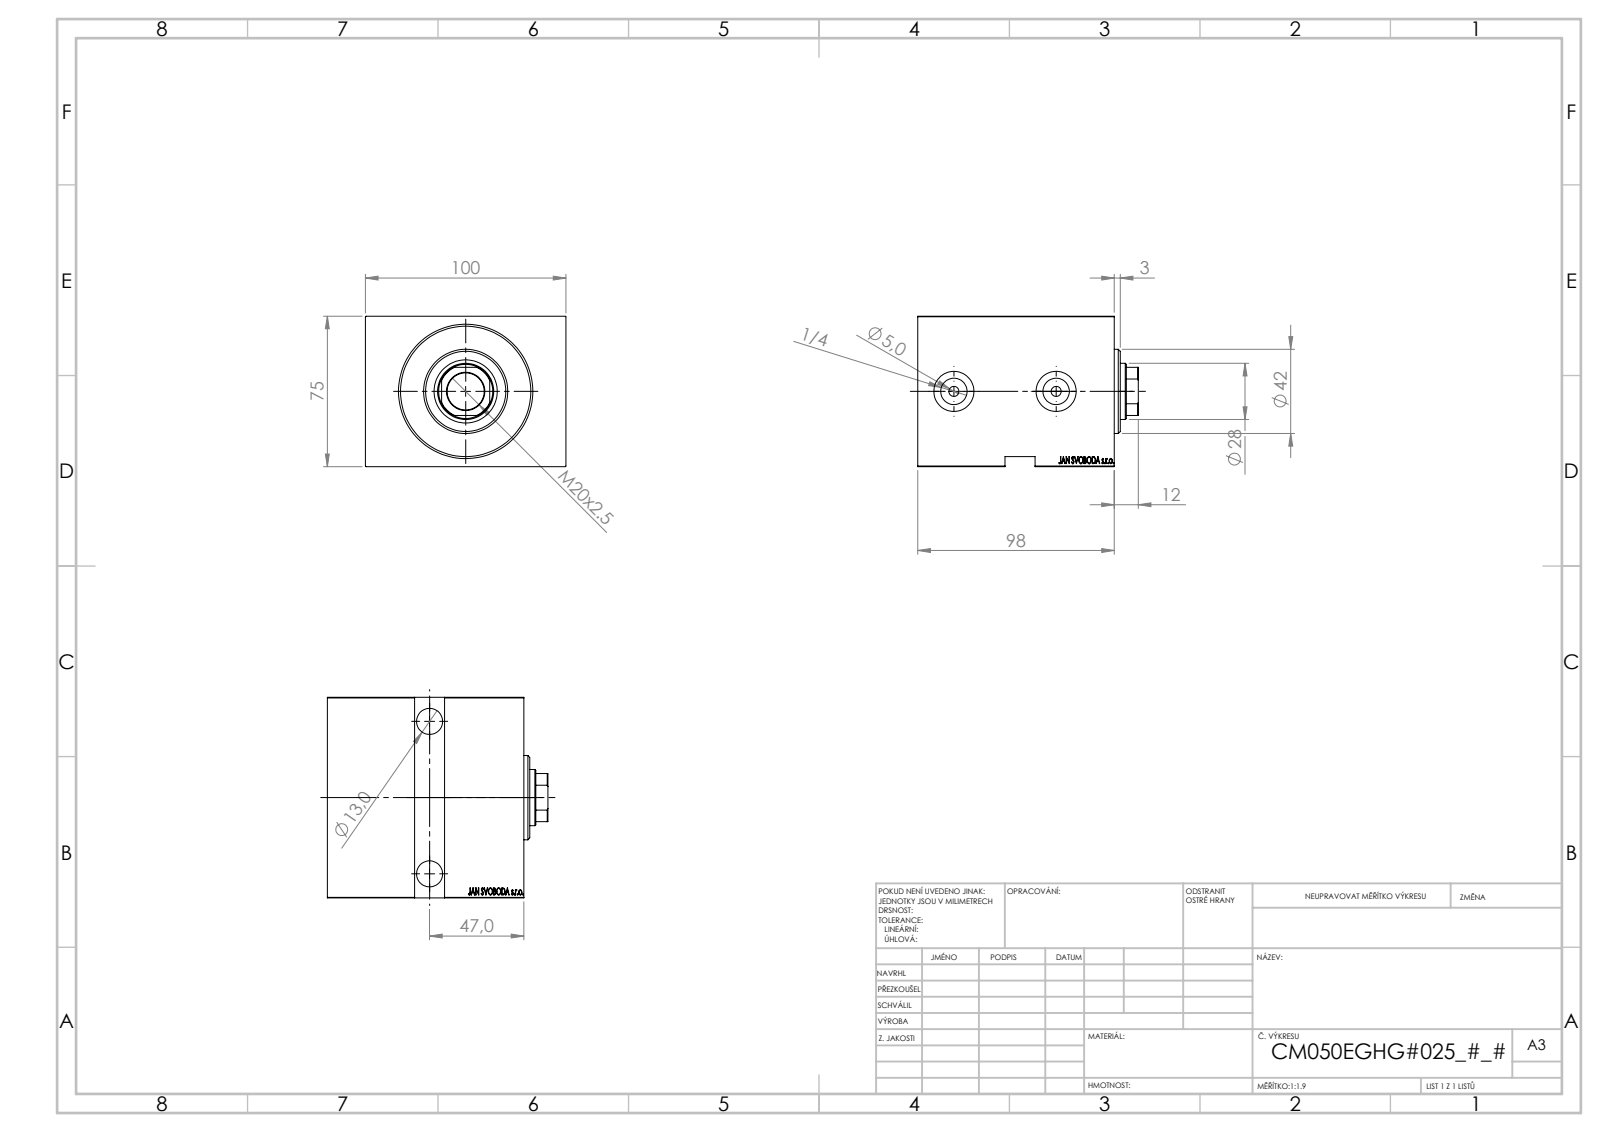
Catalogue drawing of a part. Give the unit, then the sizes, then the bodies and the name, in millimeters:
Units: millimetres
Overall size (bounding box): 110 × 100 × 75
Round holes (diameter × count): ⌀5 ×2, ⌀13 ×2, ⌀13.16 ×2, ⌀19 ×2, ⌀20 ×2, ⌀18.5 ×1, ⌀28 ×1, ⌀31.5 ×1, ⌀50 ×1, ⌀65 ×1
Round bosses / shafts (diameter × count): ⌀52 ×1, ⌀42 ×1
Partial cylindrical surfaces — rounded edges, fillets, slot ends (radius × count): R13.5 ×1
Main face-to-face distances: 75, 100, 98, 14, 84, 5, 93, 79, 81.4, 67.4
Hole centre spacings: 51, 76
Volume: 674 002 mm³ · Surface area: 98 375 mm²
Bodies: 3 solids, 846 faces (408 planar, 44 cylindrical, 394 other)
Part name (STEP PRODUCT): V450CM_E_Body; V450CM_E_VCP; V450CM_VC_B
STEP written by: SolidWorks 2019 (CONFIG_CONTROL_DESIGN)
